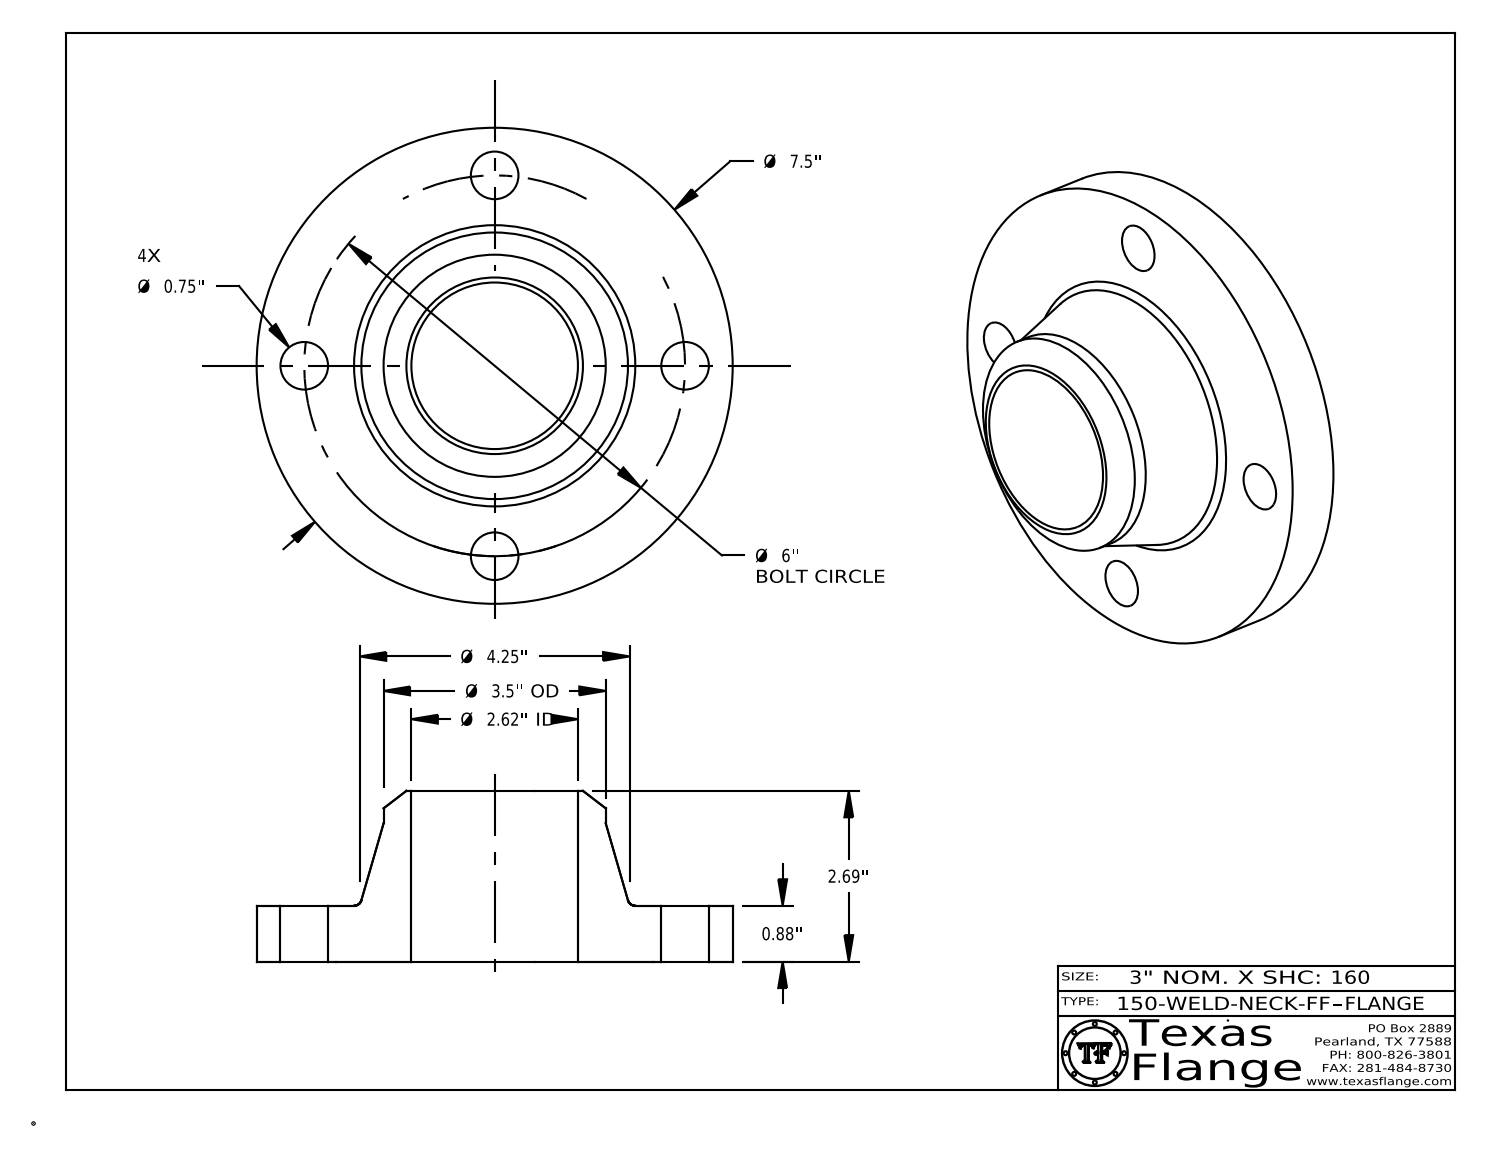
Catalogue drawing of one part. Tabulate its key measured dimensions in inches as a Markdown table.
| quantity | value |
| --- | --- |
| part name | 150-WELD-NECK-FF |
| STEP written by | CATIA V5 STEP AP214 (AUTOMOTIVE_DESIGN) |
| units | inches |
| bodies | 1 solid, 409 faces (369 planar, 34 cylindrical, 6 other) |
| overall size | 7.5 × 7.5 × 2.69 |
| volume | 42.57 in³ |
| surface area | 140.4 in² |
| round holes (diameter × count) | 0.75 × 4, 0.495 × 1, 2.624 × 1 |
| round bosses / shafts (diameter × count) | 0.03 × 8, 7.5 × 1, 3.5 × 1, 0.39 × 1 |
| main face-to-face distances | 0.88, 2.69, 1.81, 0.865, 0.015, 1.825, 0.148, 0.144, 0.027, 0.096 |
| hole center spacings | 3, 4.243, 2.296, 5.543, 6 |
